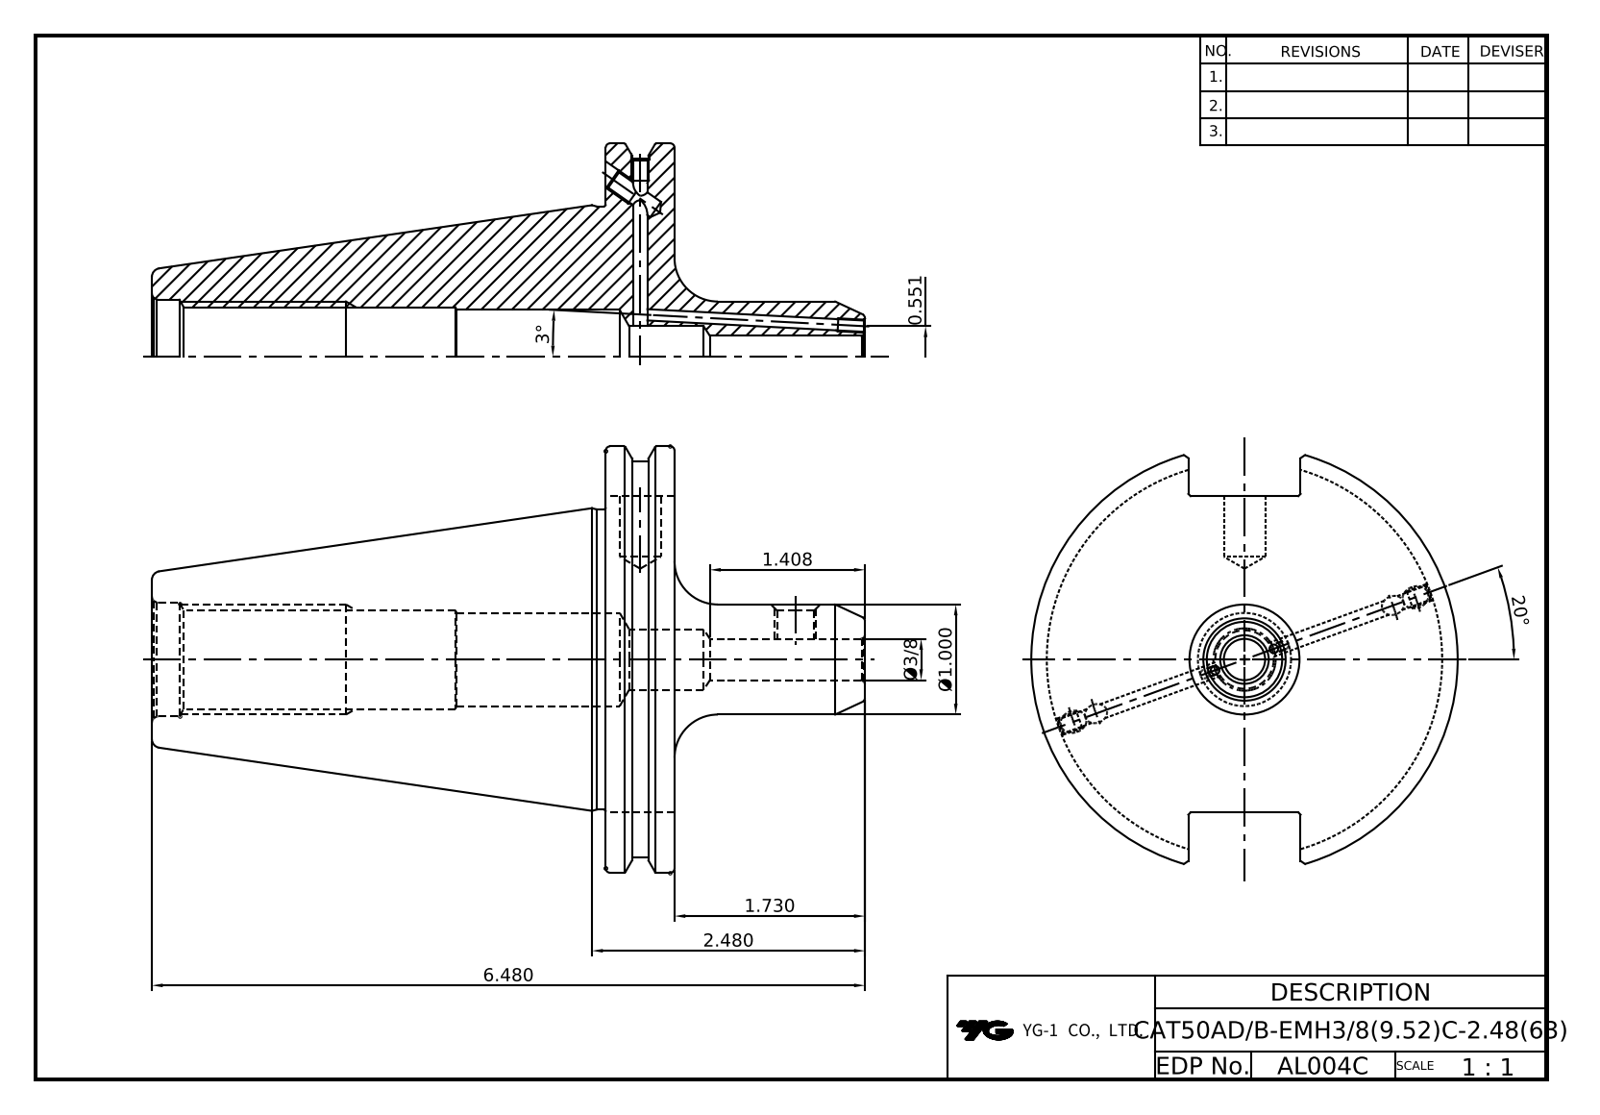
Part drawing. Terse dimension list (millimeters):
name: LO-CAT50ADB-EMH9.525C-63
written by: Autodesk Inventor 2025 (AUTOMOTIVE_DESIGN)
unit: mm
bodies: 1 solid, 88 faces (36 planar, 28 cylindrical, 24 other)
size: 164.6 × 98.42 × 94.69
volume: 338 208 mm³; area: 50 578 mm²
holes: 2× ⌀2.46, 2× ⌀3.24, 2× ⌀4.13, 2× ⌀4.2, 2× ⌀5, 2× ⌀9.53, 1× ⌀8.38, 1× ⌀14, 1× ⌀21.97, 1× ⌀26.2
bosses: 1× ⌀98.42, 1× ⌀91.29, 1× ⌀69.25, 1× ⌀25.4
face distances: 15.88, 104.77, 120.65, 73.03, 25.9, 114.64, 9.87, 6.01, 110.81, 6.04
hole spacings: 35.87
